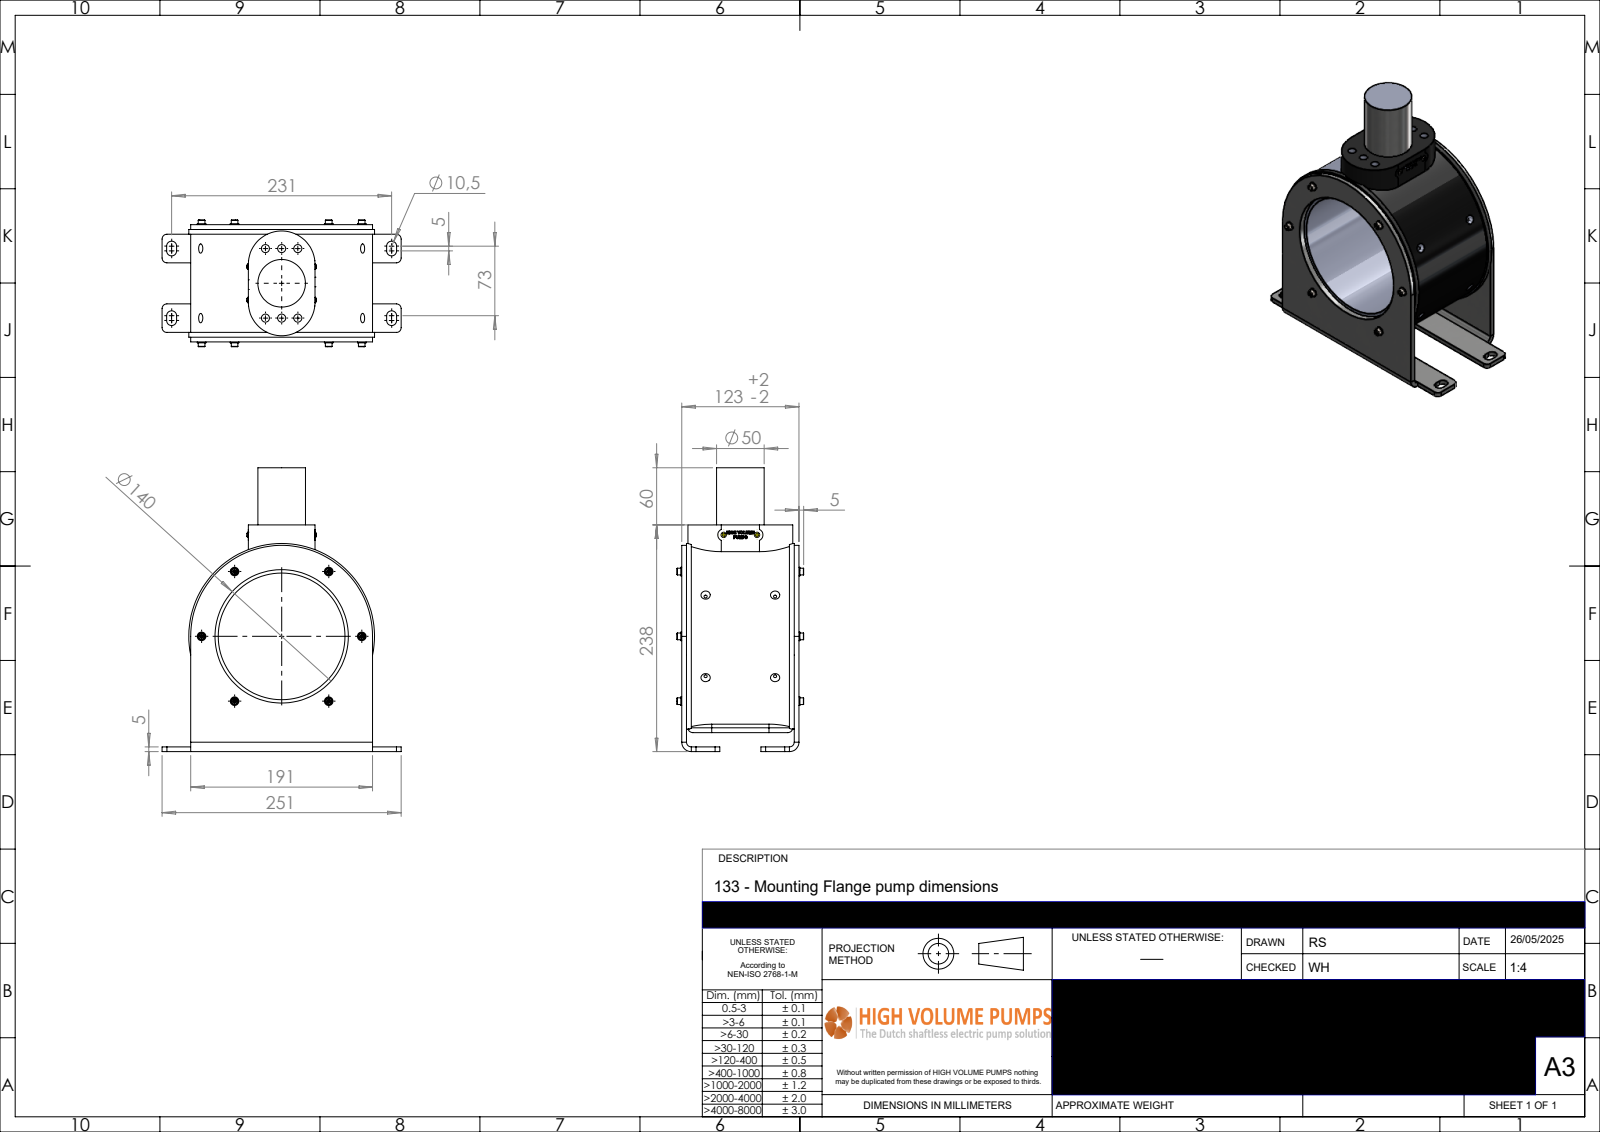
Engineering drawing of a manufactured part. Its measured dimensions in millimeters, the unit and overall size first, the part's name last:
Units: millimetres
Overall size (bounding box): 298 × 251 × 133.06
Round holes (diameter × count): ⌀8.5 ×6, ⌀3.3 ×4, ⌀133 ×1, ⌀140 ×1
Round bosses / shafts (diameter × count): ⌀9 ×6, ⌀7 ×6, ⌀7.64 ×2, ⌀5.7 ×2, ⌀195 ×1, ⌀191 ×1, ⌀50 ×1
Partial cylindrical surfaces — rounded edges, fillets, slot ends (radius × count): R5 ×14, R5.25 ×8, R6.25 ×2, R10 ×2, R25 ×2, R35 ×2, R1 ×1
Main face-to-face distances: 5, 123.06, 118.06, 113.06, 238, 233, 15, 20, 218, 10
Hole centre spacings: 73, 17, 74.95, 34, 80.53
Volume: 2 272 000 mm³ · Surface area: 250 206 mm²
Bodies: 1 solid, 833 faces (567 planar, 92 cylindrical, 174 other)
Part name (STEP PRODUCT): P-133-030-rev-A-MF
STEP written by: SolidWorks 2024 (AUTOMOTIVE_DESIGN)
